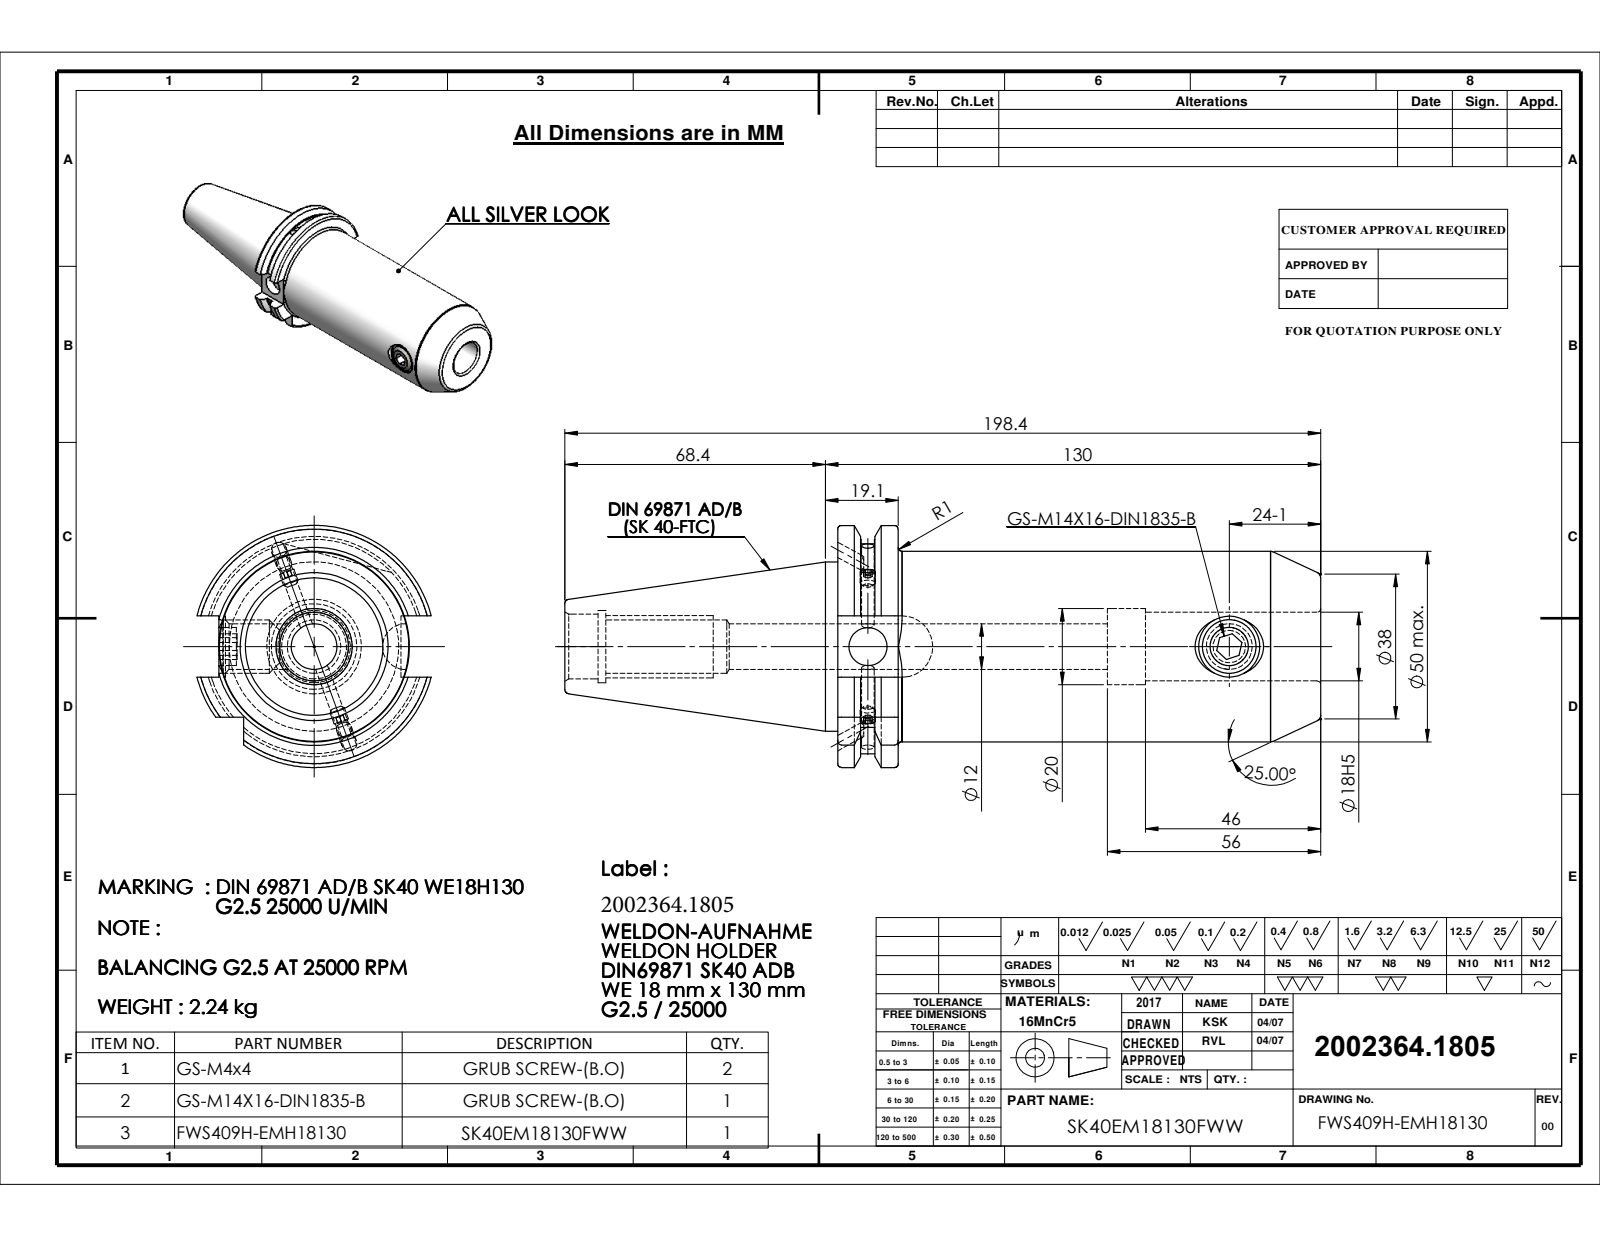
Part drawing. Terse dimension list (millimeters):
name: 91406-WE718130; M14X16_ISO 4026 - M12 x 12-N; SK40EM18130FWW; Copy of M4X4_DIN 913 - M4 x 4-N
written by: SolidWorks 2009 (CONFIG_CONTROL_DESIGN)
unit: mm
bodies: 4 solids, 163 faces (59 planar, 45 cylindrical, 59 other)
size: 198.4 × 63.55 × 61.48
volume: 290 685 mm³; area: 44 626 mm²
holes: 2× ⌀12, 1× ⌀3.3, 1× ⌀10, 1× ⌀14, 1× ⌀16, 1× ⌀17, 1× ⌀18, 1× ⌀19, 1× ⌀20
bosses: 2× ⌀4, 1× ⌀50, 1× ⌀44.45, 1× ⌀14
rounds: 1× R8.05, 1× R28.12, 1× R31.77
face distances: 126.8, 15.9, 110.9, 47.8, 70.8, 54.9, 56, 16.1, 71.6, 87.5
hole spacings: 94.85
